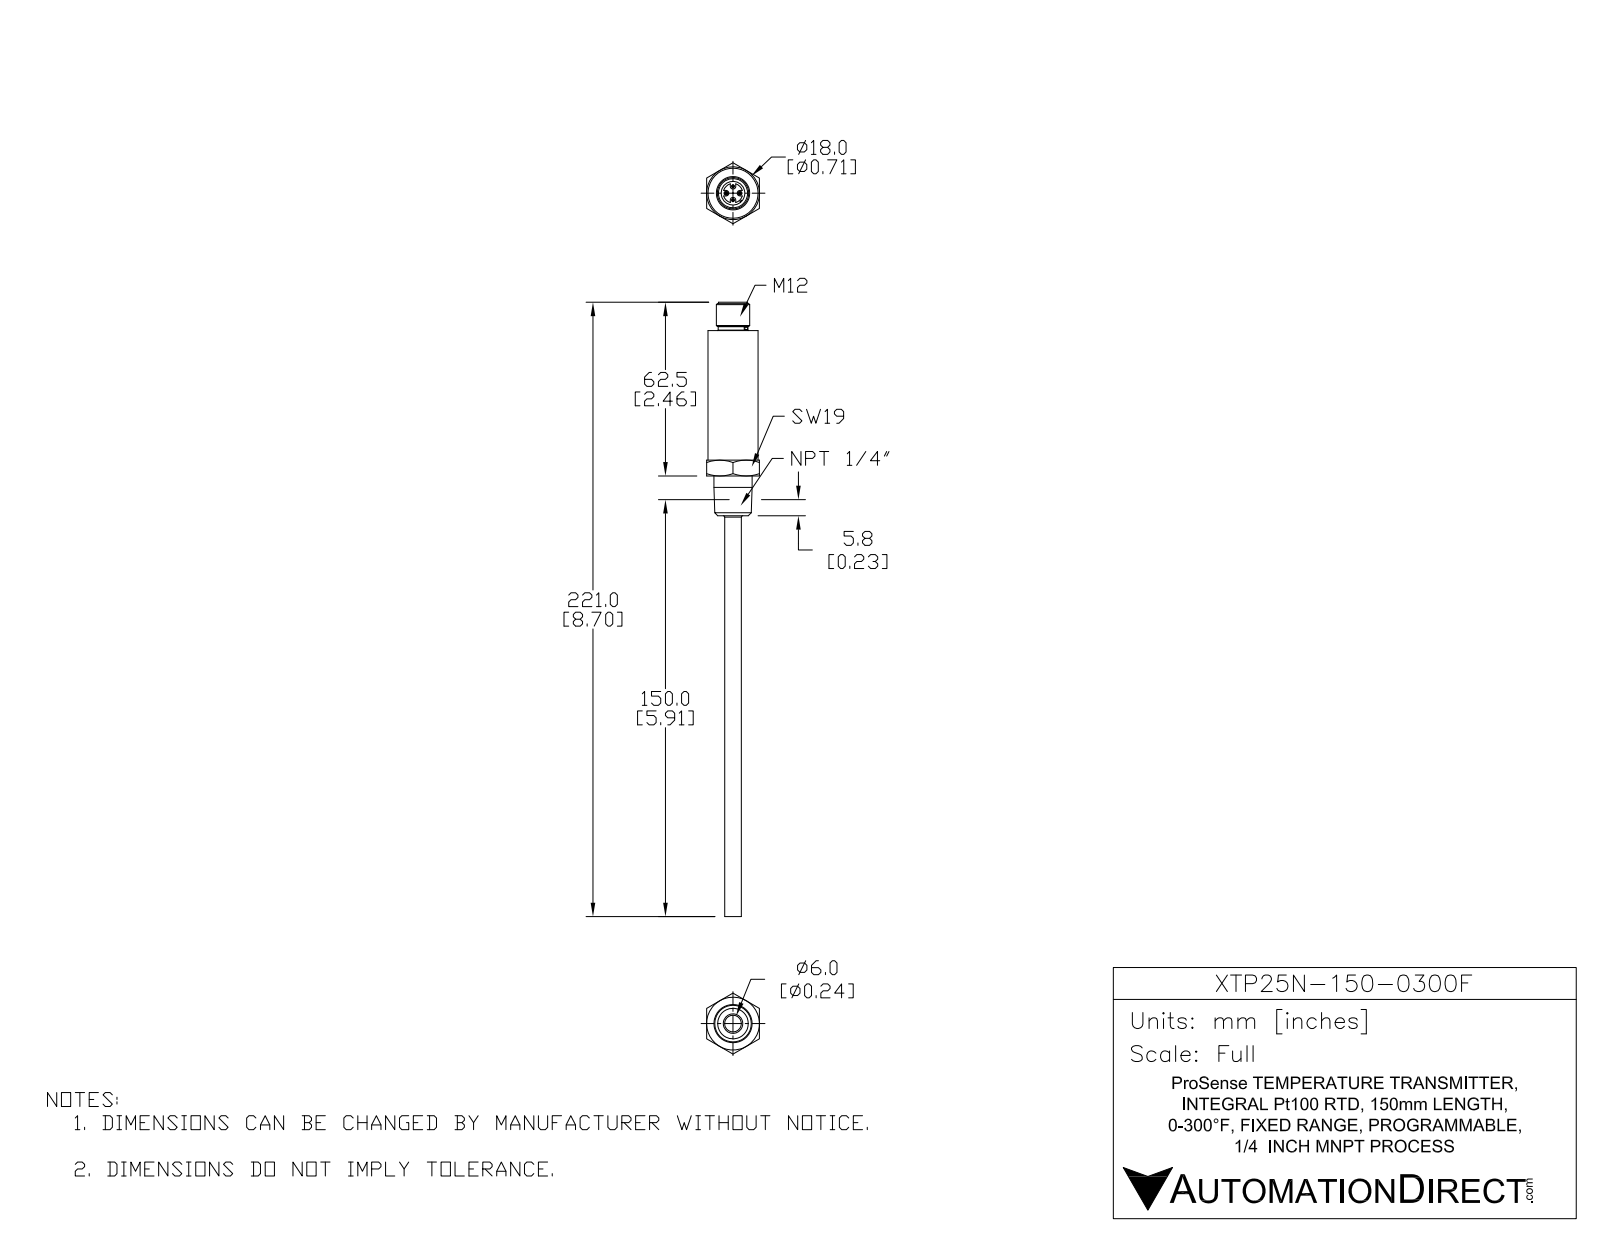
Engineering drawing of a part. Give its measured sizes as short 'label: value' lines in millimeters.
name: XTP25N-150-0300F
written by: SolidWorks 2015 (AUTOMOTIVE_DESIGN)
unit: mm
bodies: 1 solid, 117 faces (43 planar, 34 cylindrical, 40 other)
size: 221 × 21.94 × 19
volume: 20 060 mm³; area: 7 889 mm²
holes: 1× ⌀4, 1× ⌀8.5
bosses: 4× ⌀1.02, 1× ⌀18, 1× ⌀13.72, 1× ⌀12, 1× ⌀10.7, 1× ⌀10.5, 1× ⌀6
rounds: 4× R1, 1× R3.5, 1× R4.25
face distances: 19, 52.3, 14.3, 66.6, 20, 5.7, 46.6, 76.8, 62.5, 56.8
